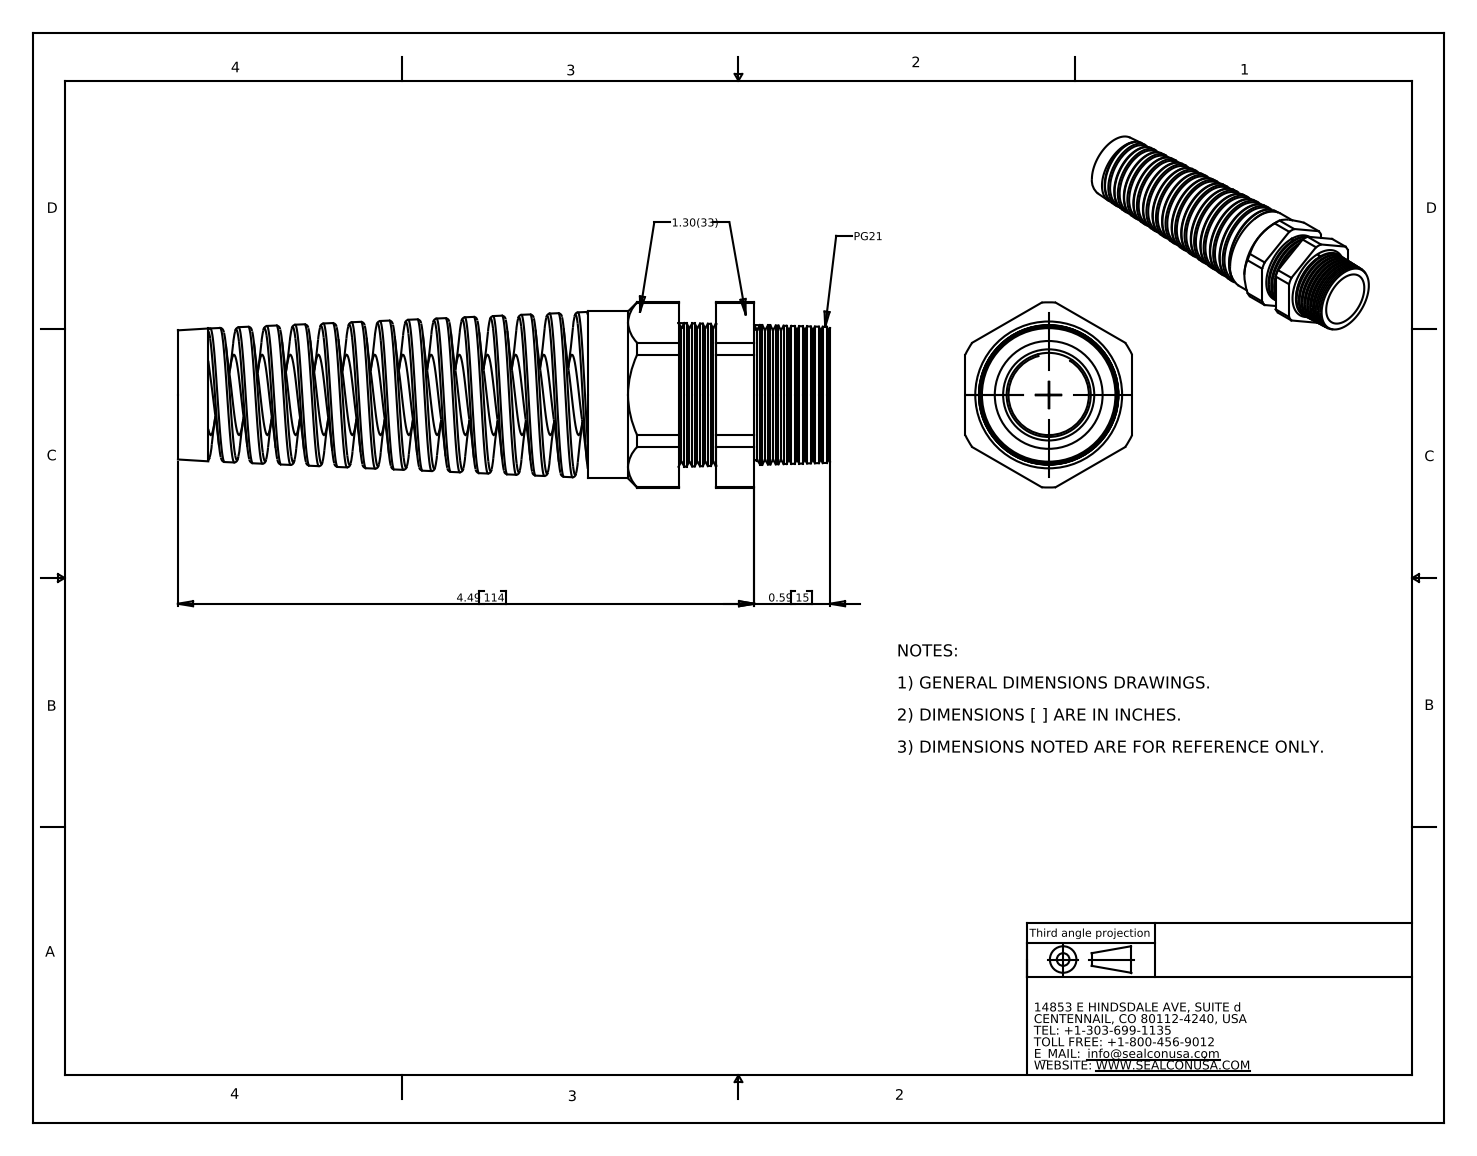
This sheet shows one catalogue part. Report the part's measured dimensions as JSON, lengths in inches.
{"part_name": "CF21CA-BK", "step_written_by": "SolidWorks 2007 (CONFIG_CONTROL_DESIGN)", "units": "inches", "bodies": {"solids": 2, "faces": 216, "planar": 24, "cylindrical": 53, "other": 139}, "overall_size": [5.08, 1.443, 1.3], "volume_in3": 2.851, "surface_area_in2": 48.66, "round_holes": [[0.626, 1], [0.655, 1], [0.71, 1]], "round_bosses_or_shafts": [[1.3, 1], [0.84, 1]], "partial_cylinders_radius": [[0.721, 1]], "face_to_face_distances": [1.3, 0.295, 3.9, 4.195, 4.491, 0.59, 0.295, 3.193, 0.707, 1.002]}
